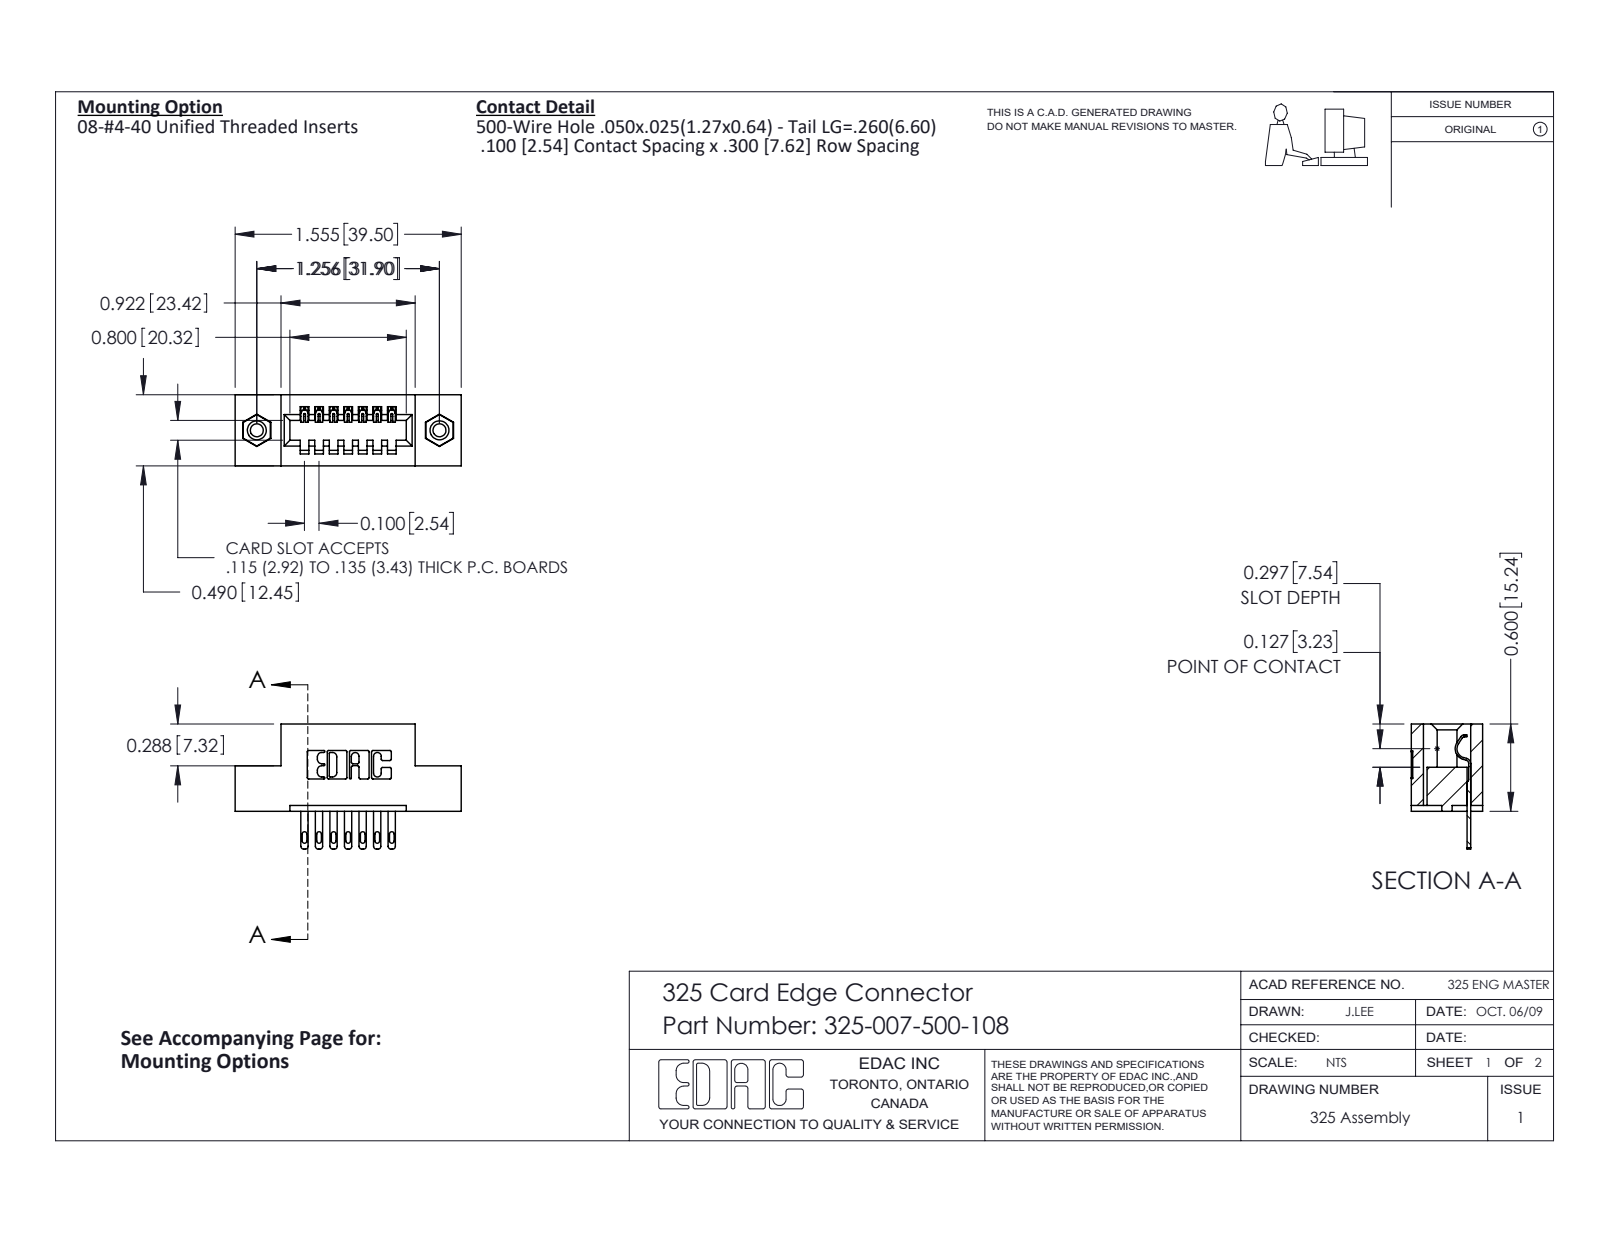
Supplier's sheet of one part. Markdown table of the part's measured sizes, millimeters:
| quantity | value |
| --- | --- |
| part name | 325-007-500-108; 325 Part_TI; 345-250-001_345-250-003-102; 325-292-001_325-293-100 |
| STEP written by | SolidWorks 2016 (CONFIG_CONTROL_DESIGN) |
| units | millimeters |
| bodies | 10 solids, 552 faces (354 planar, 182 cylindrical, 16 other) |
| overall size | 39.5 × 21.8 × 12.4 |
| volume | 4 740 mm³ |
| surface area | 4 613 mm² |
| round holes (diameter × count) | 2.3 × 2, 3.2 × 2, 4.1 × 2 |
| round bosses / shafts (diameter × count) | 3.9 × 2 |
| partial cylindrical surfaces (radius × count) | 0.3 × 22, 0.2 × 14, 0.4 × 14, 0.5 × 14, 0.2 × 6, 0.8 × 6, 0.7 × 3, 0.4 × 1 |
| main face-to-face distances | 7.6, 2.5, 5.1, 1, 2.1, 10.3, 12.4, 1.5, 4.1, 10.2 |
| hole center spacings | 31.9 |
